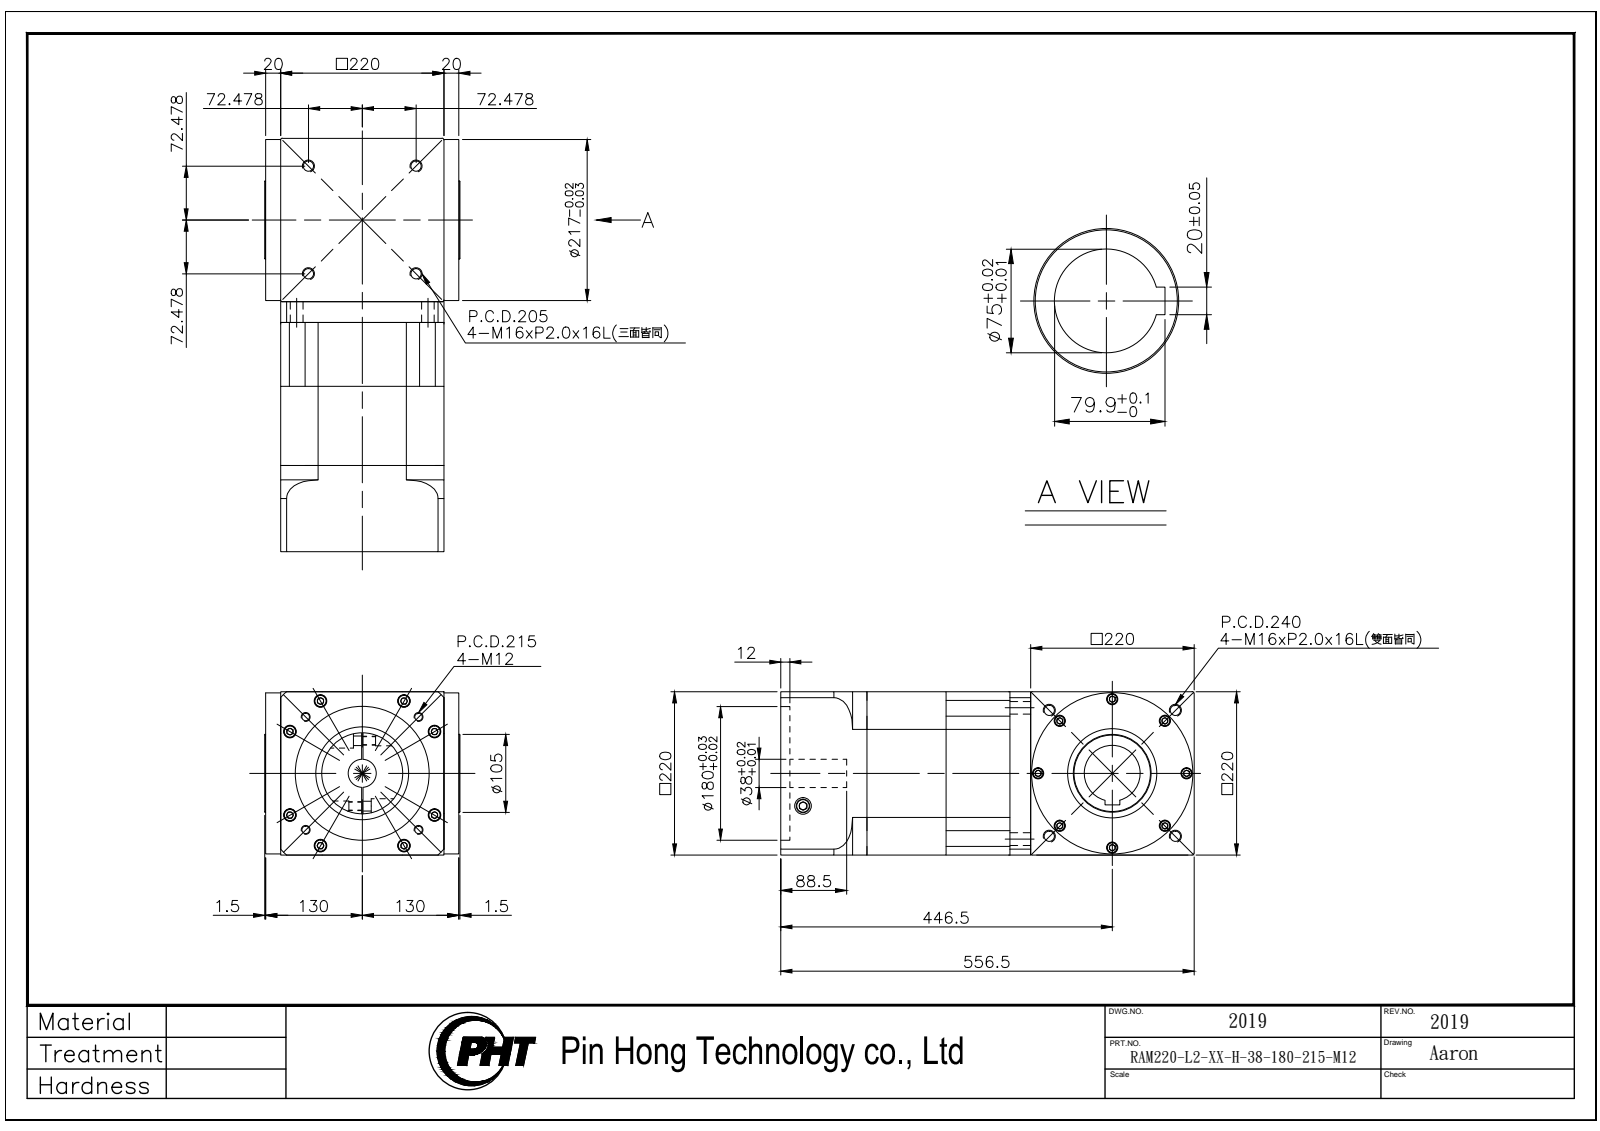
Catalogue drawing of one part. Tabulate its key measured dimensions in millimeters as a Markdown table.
| quantity | value |
| --- | --- |
| part name | RAM220-L2-XX-H-38-180-215-M12_2019 |
| STEP written by | SolidWorks 2016 (AUTOMOTIVE_DESIGN) |
| units | millimeters |
| bodies | 5 solids, 956 faces (448 planar, 320 cylindrical, 188 other) |
| overall size | 556.5 × 263 × 220 |
| volume | 25 640 000 mm³ |
| surface area | 1 221 000 mm² |
| round holes (diameter × count) | 9 × 12, 14 × 12, 15 × 12, 17 × 12, 11 × 8, 10.2 × 4, 22.5 × 2, 38 × 1, 75 × 1, 76 × 1, 125 × 1, 180 × 1 |
| round bosses / shafts (diameter × count) | 13 × 12, 16 × 8, 24 × 4, 217 × 1, 120 × 1, 109 × 1, 105 × 1 |
| partial cylindrical surfaces (radius × count) | 15 × 4, 125 × 1, 150 × 1 |
| main face-to-face distances | 220, 192.5, 106.5, 86, 220.5, 114, 28, 248, 20, 440.5 |
| hole center spacings | 100, 51.76, 112.5, 141.42, 173.2, 193.18, 29.14, 29.76 |
